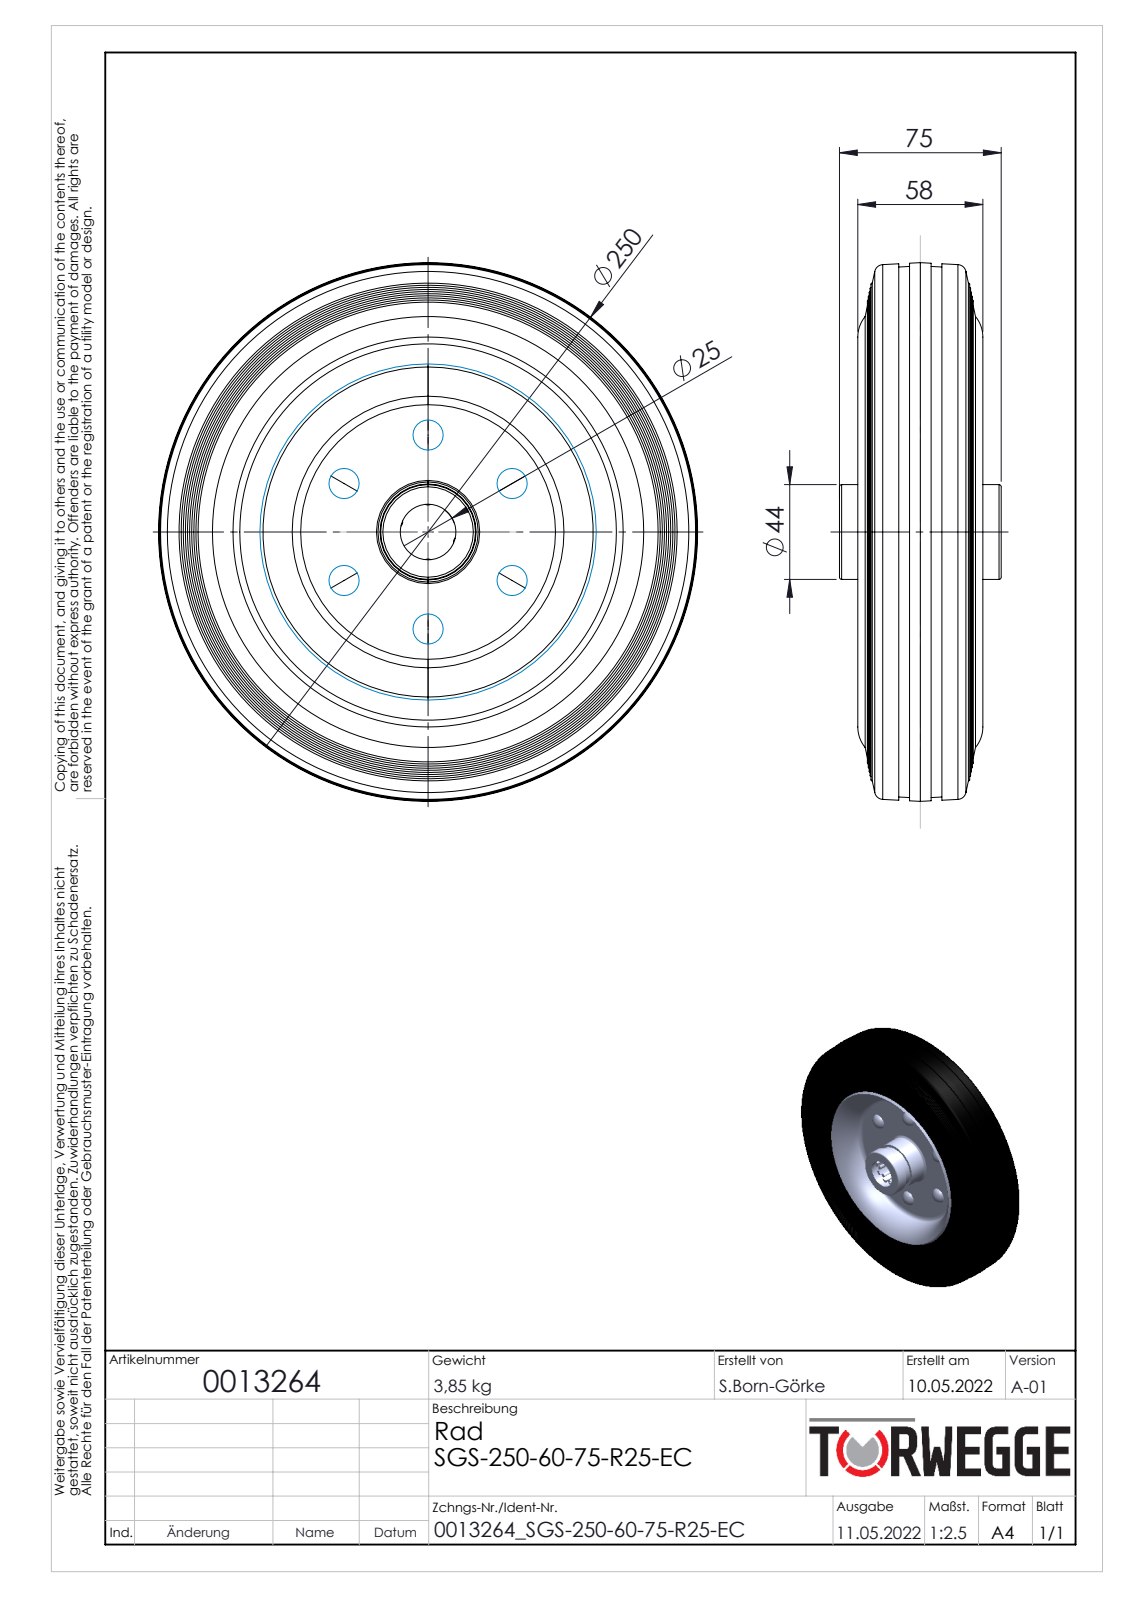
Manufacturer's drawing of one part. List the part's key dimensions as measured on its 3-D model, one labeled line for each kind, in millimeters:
Part name (STEP PRODUCT): 0013264
STEP written by: SolidWorks 2020 (AUTOMOTIVE_DESIGN)
Units: millimetres
Bodies: 0 solids, 219 faces (53 planar, 0 cylindrical, 166 other)
Overall size (bounding box): 250 × 250 × 75
Main face-to-face distances: 5, 7.5, 26.5, 31.5, 32.5, 15, 2.5, 10, 40, 47.5
